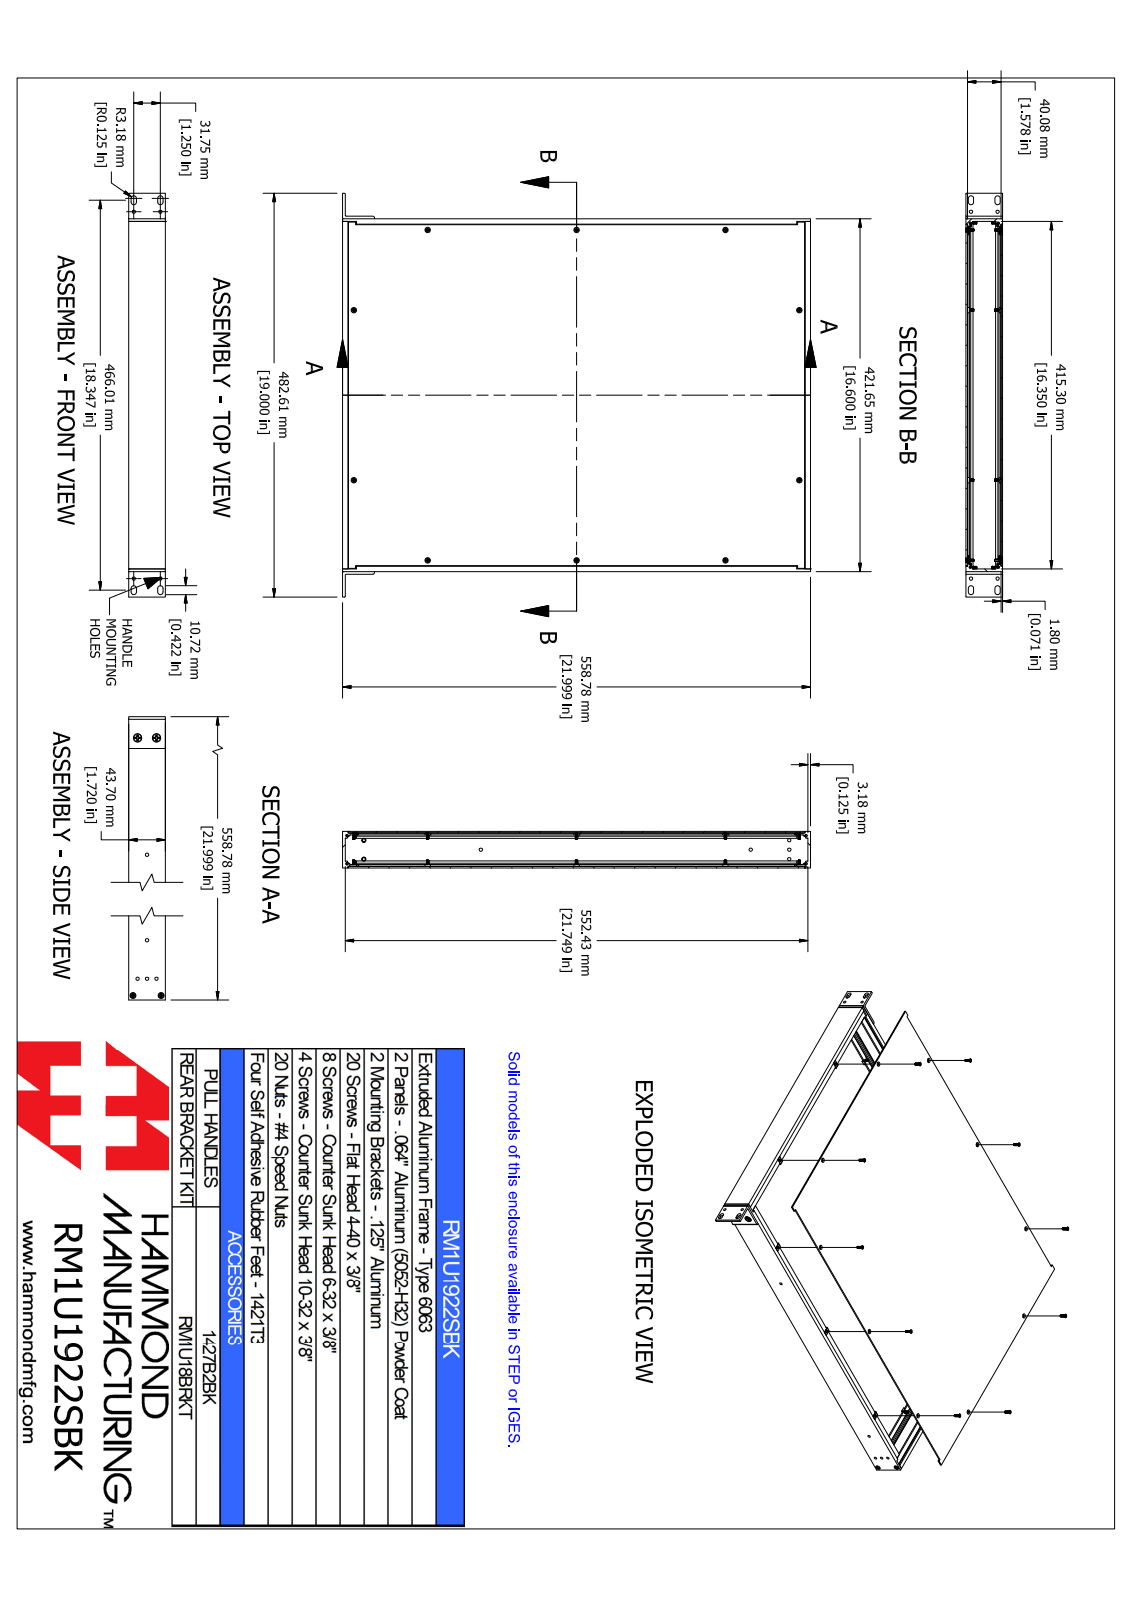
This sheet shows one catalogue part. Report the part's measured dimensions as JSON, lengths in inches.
{"part_name": "RM1U1922SBK", "step_written_by": "SolidWorks 2021 (AUTOMOTIVE_DESIGN)", "units": "inches", "bodies": {"solids": 60, "faces": 2972, "planar": 952, "cylindrical": 708, "other": 1312}, "overall_size": [21.999, 19, 1.72], "volume_in3": 76.25, "surface_area_in2": 1892, "round_holes": [[0.157, 10], [0.16, 10], [0.165, 6], [0.138, 4], [0.156, 4], [0.157, 4], [0.169, 4], [0.159, 3], [0.197, 2]], "round_bosses_or_shafts": [[0.2, 10], [0.112, 10], [0.238, 5], [0.138, 5], [0.36, 2], [0.19, 2]], "partial_cylinders_radius": [[0.01, 80], [0.024, 80], [0.009, 40], [0.014, 40], [0.015, 16], [0.038, 16], [0.039, 14], [0.035, 8]], "face_to_face_distances": [0.071, 1.649, 1.72, 1.578, 0.125, 16.476, 0.087, 1.633, 0.016, 1.562], "hole_center_spacings": [7, 5.127, 17.049, 8, 11.131, 12.274, 14, 15.756]}
